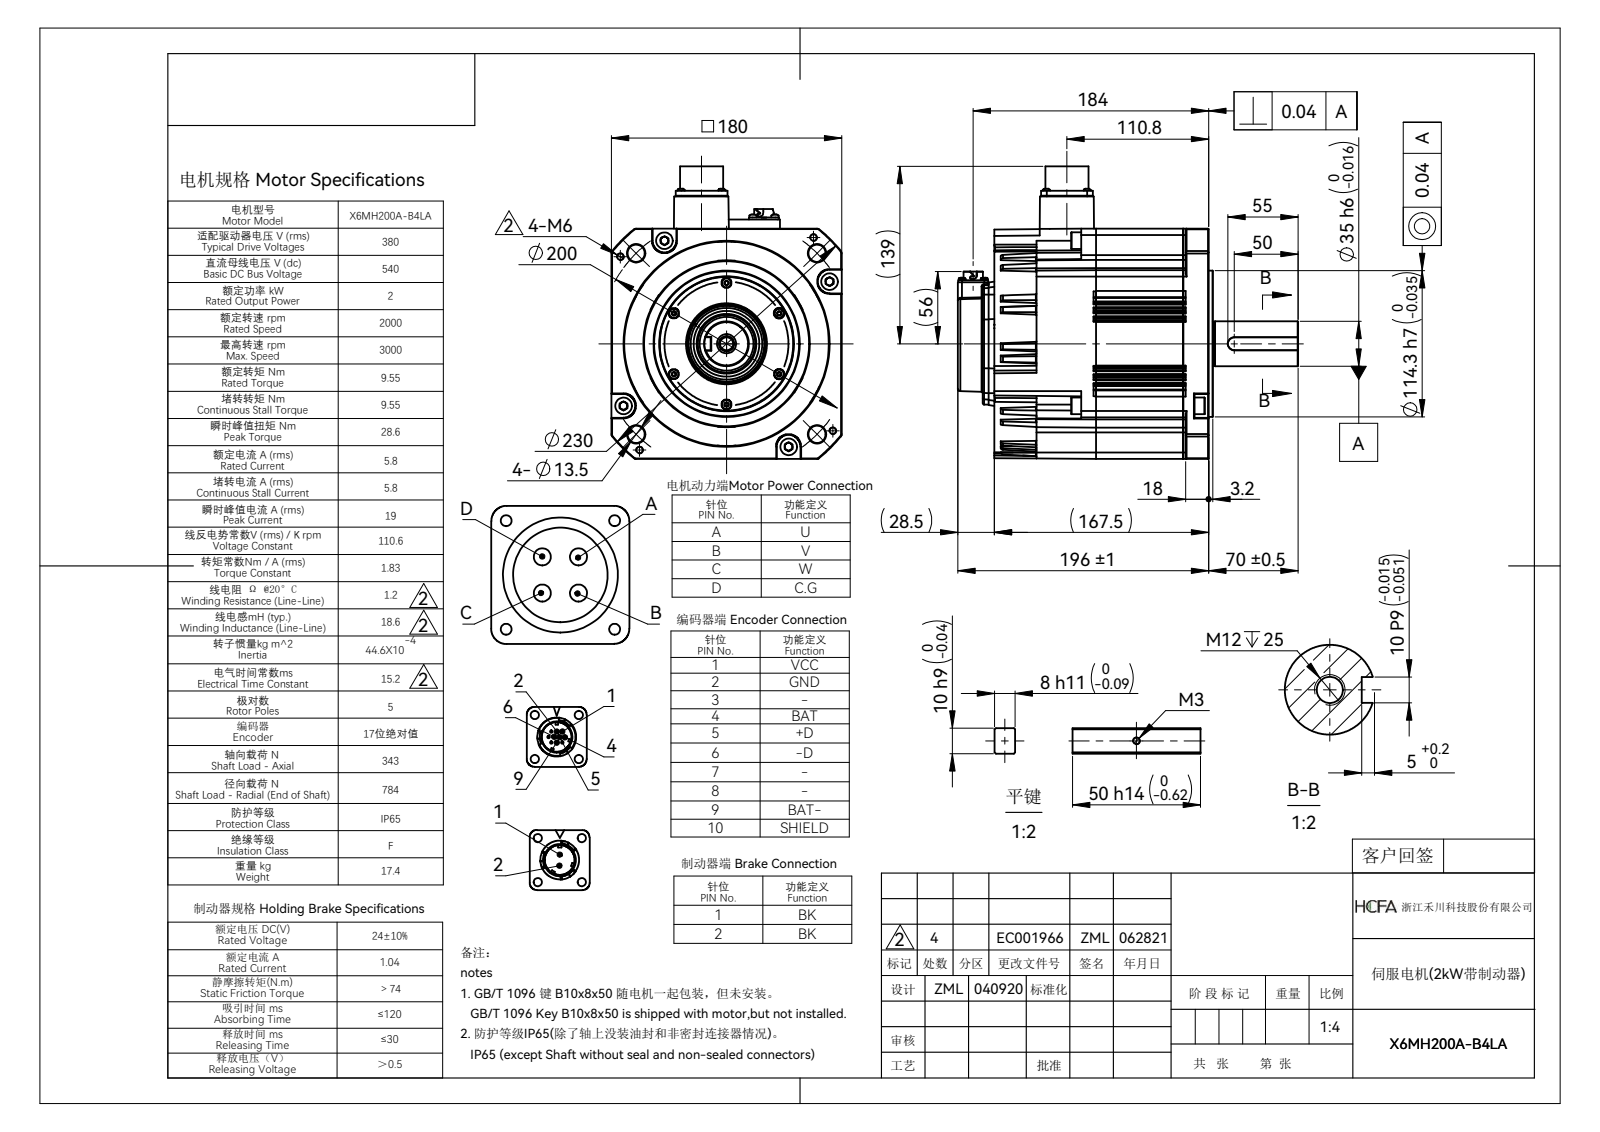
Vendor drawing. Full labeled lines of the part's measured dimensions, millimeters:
Part name (STEP PRODUCT): SV-X2MH200A-B4LA
STEP written by: SolidWorks 2016 (CONFIG_CONTROL_DESIGN)
Units: millimetres
Bodies: 1 solid, 2096 faces (809 planar, 689 cylindrical, 598 other)
Overall size (bounding box): 266 × 228.55 × 180
Volume: 4 838 000 mm³ · Surface area: 239 589 mm²
Round holes (diameter × count): ⌀13.5 ×4, ⌀11.6 ×2, ⌀10.2 ×1, ⌀11.75 ×1, ⌀11.8 ×1, ⌀27.7 ×1, ⌀32.5 ×1
Round bosses / shafts (diameter × count): ⌀1 ×10, ⌀5.7 ×8, ⌀13 ×4, ⌀5.6 ×4, ⌀5 ×4, ⌀15.2 ×2, ⌀0.75 ×2, ⌀114.3 ×1
Partial cylindrical surfaces — rounded edges, fillets, slot ends (radius × count): R0.5 ×105, R1 ×48, R5 ×29, R2 ×18, R0.55 ×16, R0.2 ×8, R3 ×8, R2.8 ×4
Main face-to-face distances: 180, 32.5, 167.5, 170.7, 3.2, 147.5, 4, 163.5, 7.2, 115
Hole centre spacings: 100, 141.42, 200, 48.75, 75.81, 78.87
